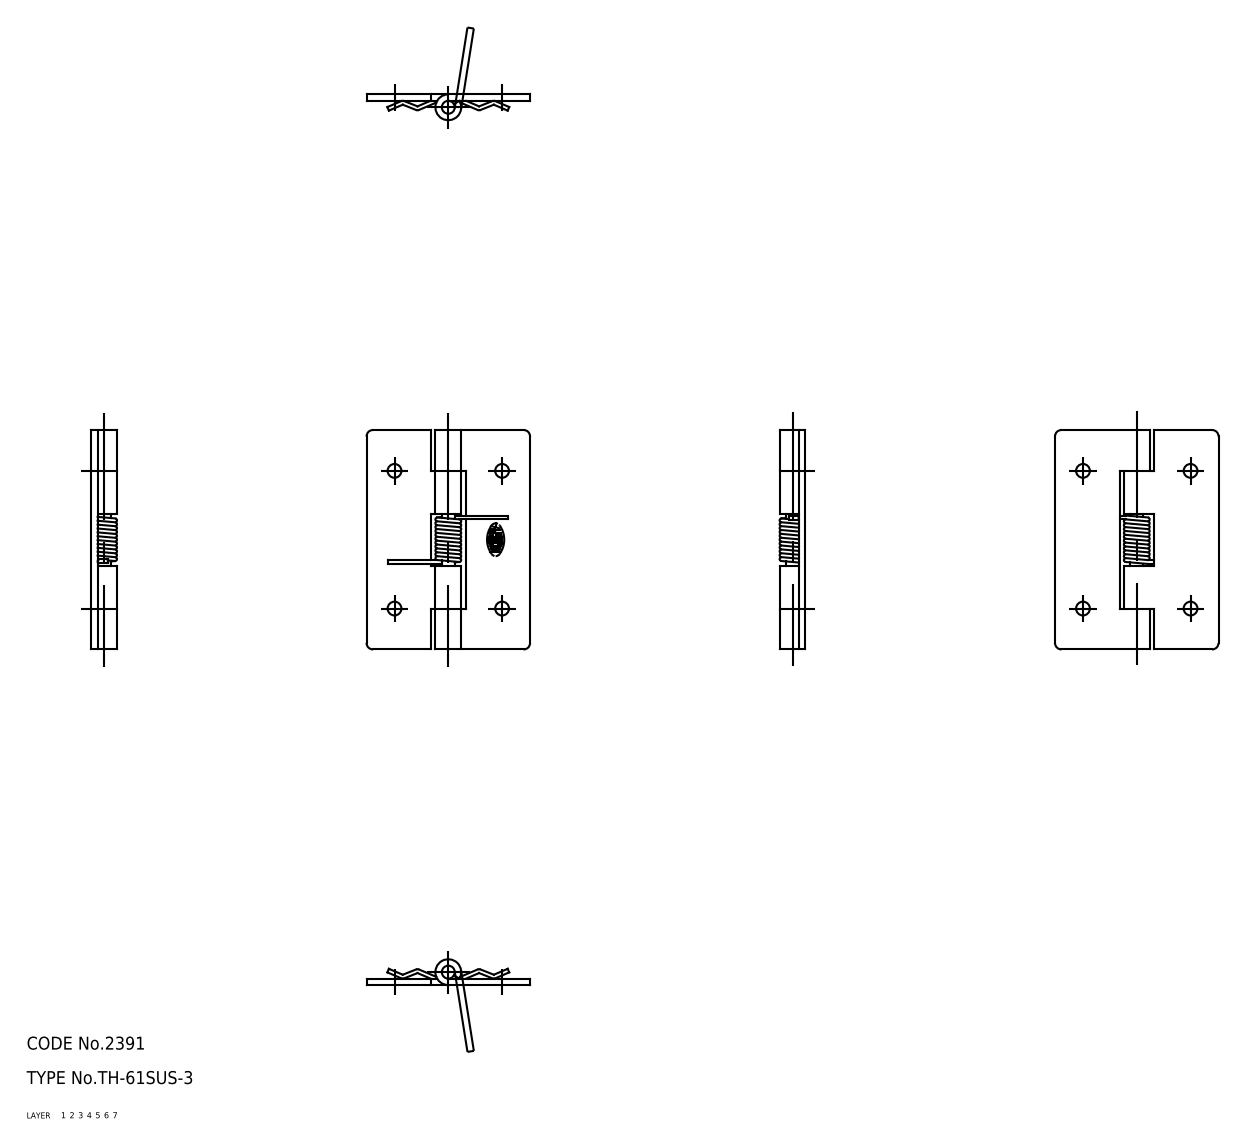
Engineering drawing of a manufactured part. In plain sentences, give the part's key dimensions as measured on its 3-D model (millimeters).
The part is named "spring; shaft; hinge piece_B; hinge piece_A (+1 more)". Its 3-D file was written by "CADfix (AUTOMOTIVE_DESIGN)". It is 4 solids with 77 faces: 0 planar, 0 cylindrical and 77 other. Overall it measures 51 by 38 by 6 millimeters. Its volume is 3 649 cubic millimeters and its surface area 5 899 square millimeters.
